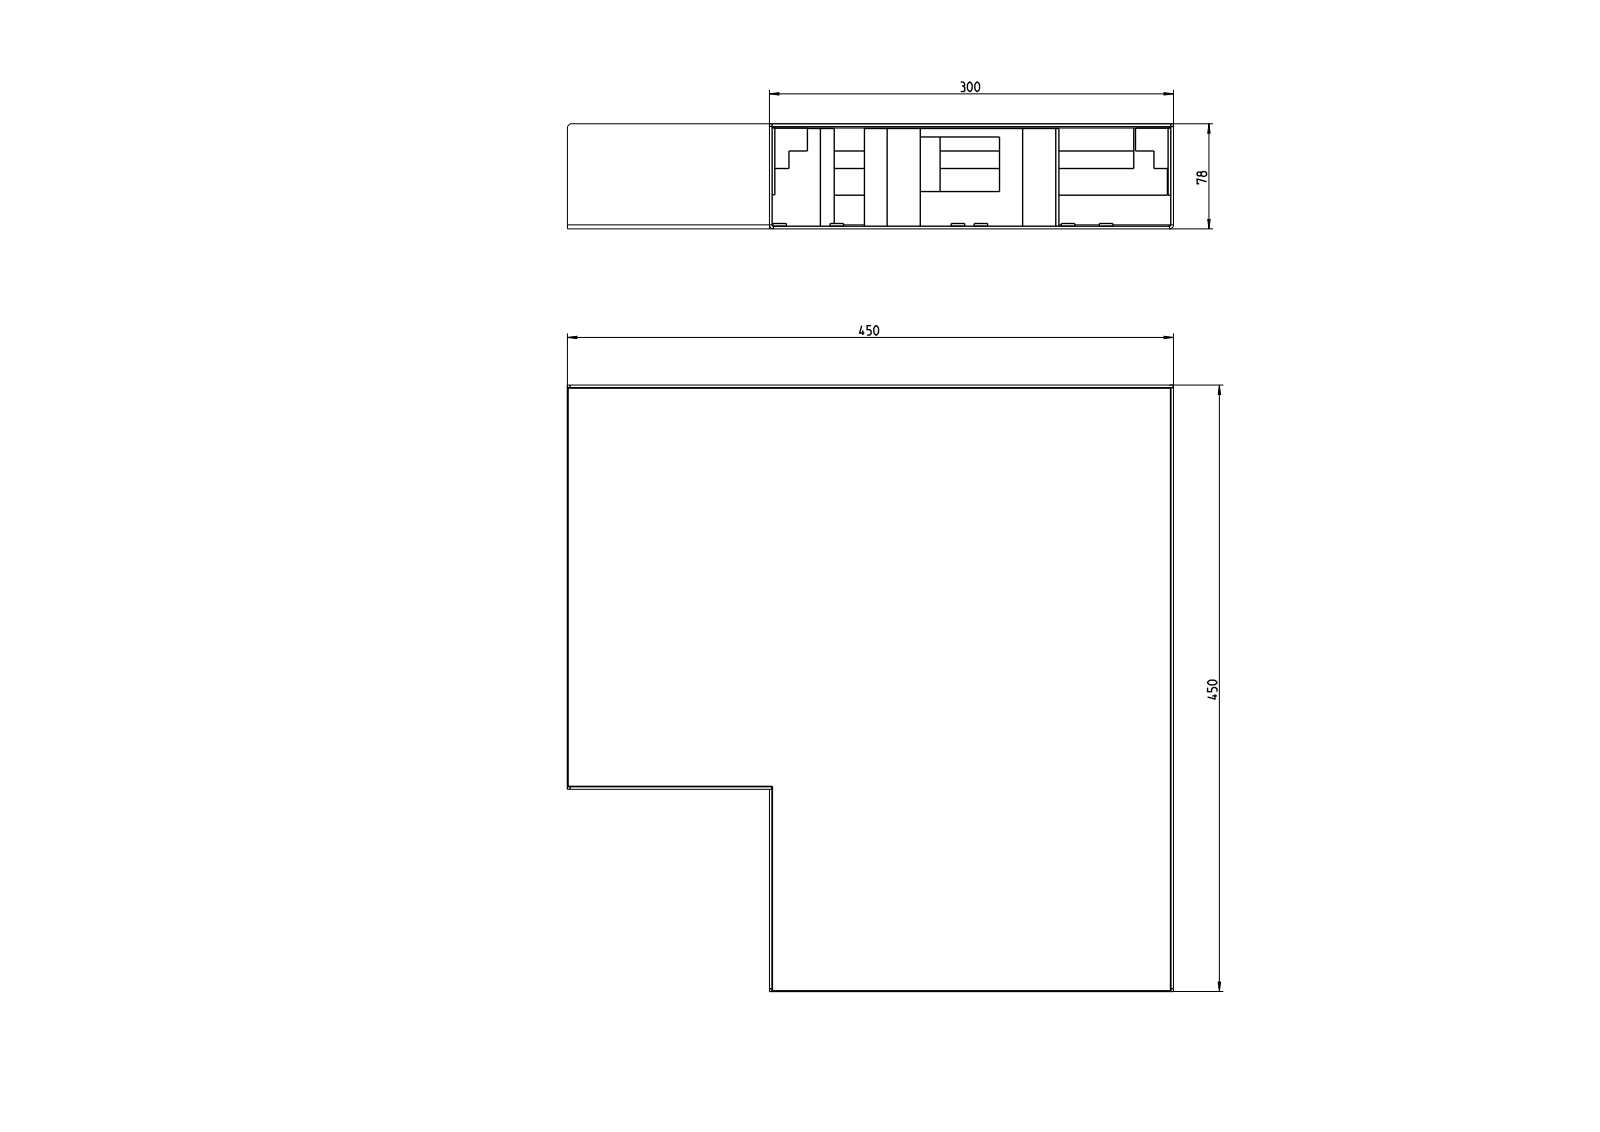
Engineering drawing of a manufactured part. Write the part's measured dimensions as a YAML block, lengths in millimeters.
part_name: "T-01225; T-01218; T-01248; T-01247 (+8 more)"
step_written_by: "CREO PARAMETRIC BY PTC INC, 2022024 (AUTOMOTIVE_DESIGN)"
units: millimeters
bodies: {solids: 16, faces: 416, planar: 273, cylindrical: 95, other: 48}
overall_size: [641.41, 611.77, 78.23]
volume: 2630000
surface_area: 1415000
round_holes:
  - {diameter: 6, count: 12}
  - {diameter: 6.5, count: 8}
  - {diameter: 13.6, count: 5}
round_bosses_or_shafts:
  - {diameter: 10, count: 12}
partial_cylinders:
  - {radius: 1, count: 4}
  - {radius: 3, count: 4}
face_to_face_distances: [2, 72.8, 1, 73.8, 74.8, 75.8, 4, 296, 294, 298]
hole_center_spacings: [20, 200, 97.57, 201, 222.53, 370.36, 33, 53]
